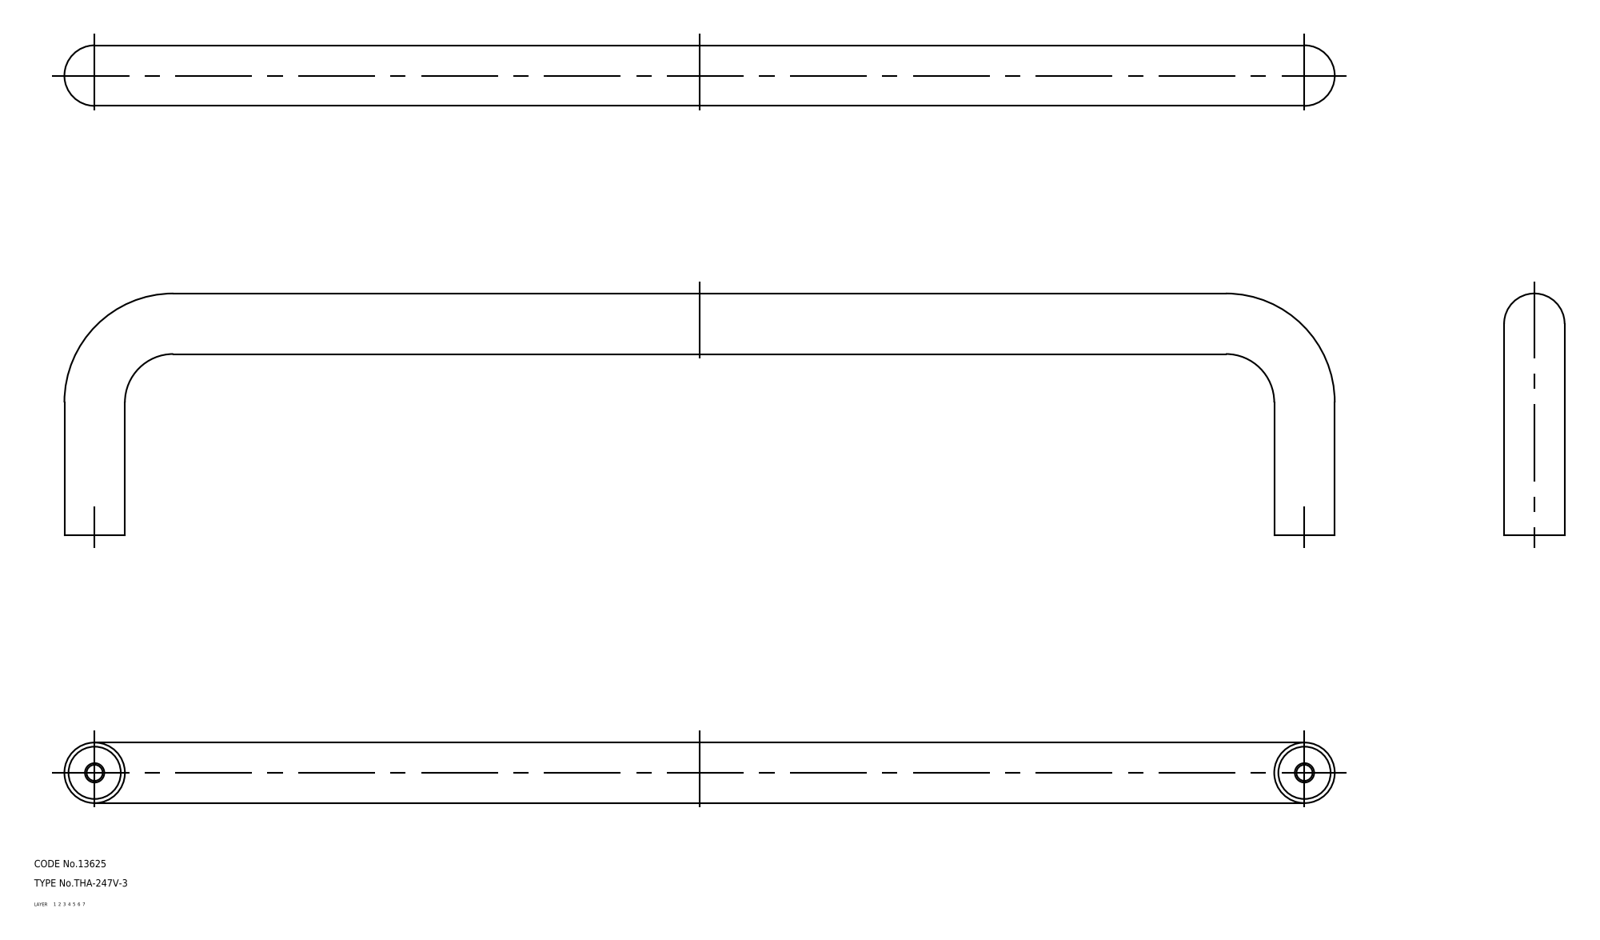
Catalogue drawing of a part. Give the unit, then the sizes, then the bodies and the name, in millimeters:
Units: millimetres
Overall size (bounding box): 525 × 100 × 25
Volume: 90 803 mm³ · Surface area: 99 341 mm²
Bodies: 3 solids, 34 faces (0 planar, 0 cylindrical, 34 other)
Part name (STEP PRODUCT): 67111346; 67111359; 67111372
STEP written by: CADfix (AUTOMOTIVE_DESIGN)
